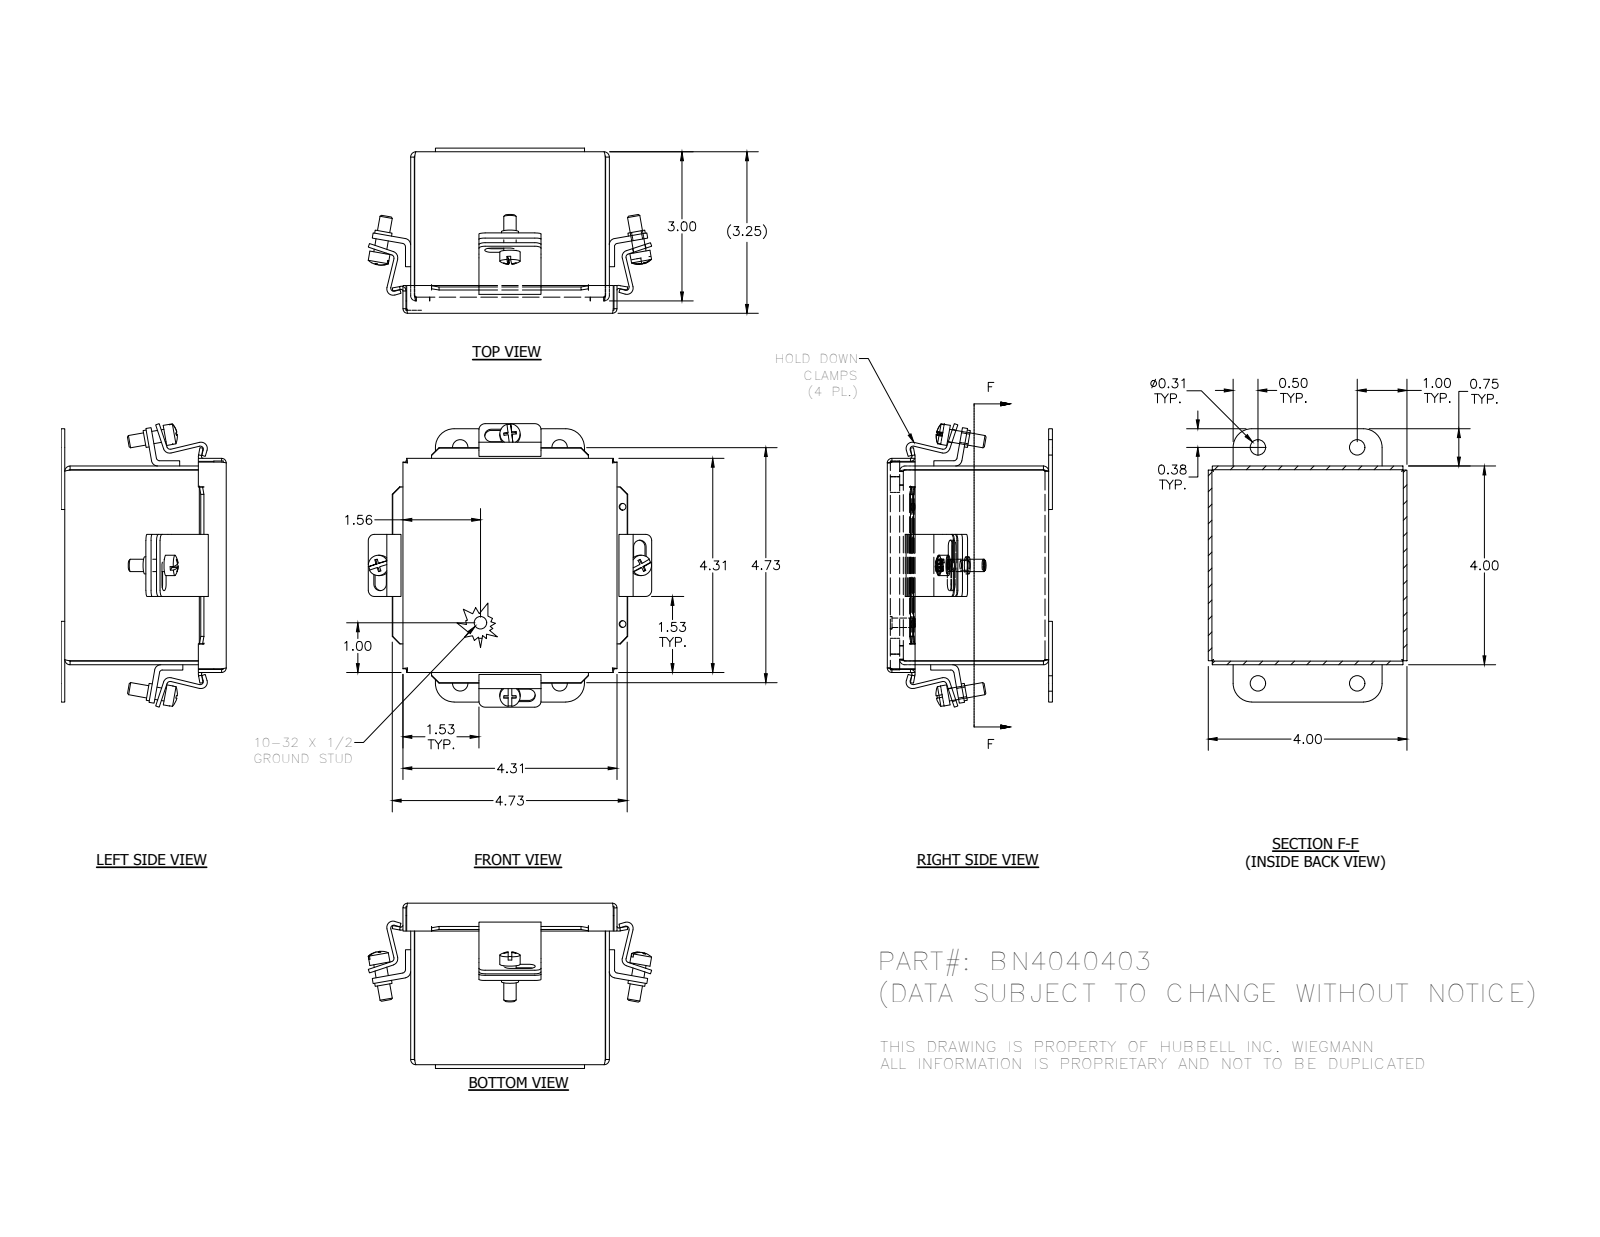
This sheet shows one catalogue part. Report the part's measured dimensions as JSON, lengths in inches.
{"part_name": "38811_1; 3481_1; C2002_1; C1001_1 (+5 more)", "step_written_by": "SolidWorks 2014 (AUTOMOTIVE_DESIGN)", "units": "inches", "bodies": {"solids": 19, "faces": 477, "planar": 283, "cylindrical": 148, "other": 46}, "overall_size": [5.705, 5.704, 3.324], "volume_in3": 10.34, "surface_area_in2": 270.4, "round_holes": [[0.196, 4], [0.31, 4], [0.136, 2]], "round_bosses_or_shafts": [[0.25, 5], [0.41, 4], [0.344, 4], [0.19, 1]], "partial_cylinders_radius": [[0.031, 16], [0.125, 16], [0.063, 12], [0.126, 12], [0.093, 8], [0.105, 8], [0.133, 8], [0.375, 4]], "face_to_face_distances": [0.074, 3.926, 3.187, 0.062, 4, 3.852, 3.25, 2.926, 0.075, 3.113], "hole_center_spacings": [2, 4.75, 5.077, 5.154, 2.36]}
